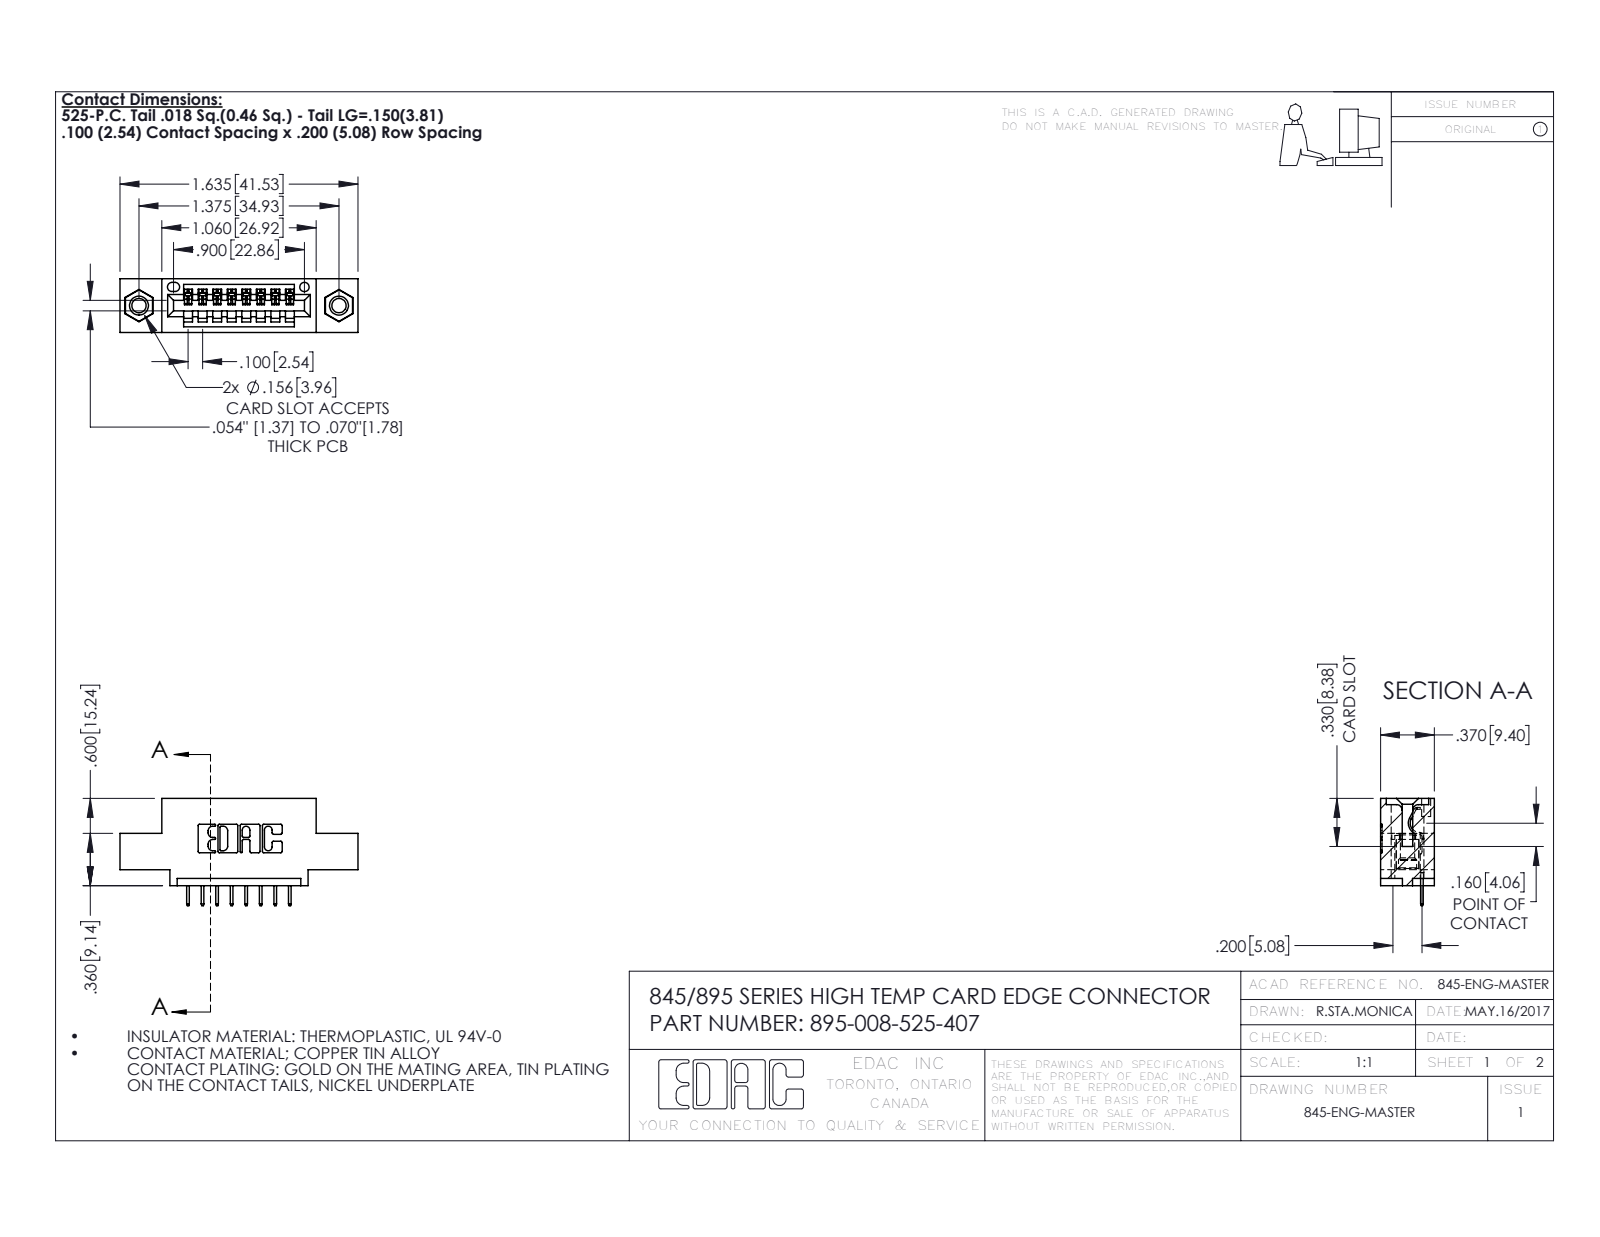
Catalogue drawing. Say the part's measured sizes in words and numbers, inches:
The part is named "895-008-525-407; 345-292-001_345-293-125; 845 Part_0.110 Offset - 0.156 Dia-TI; 345-250-001_345-250-005-103". Its 3-D file was written by "SolidWorks 2020 (CONFIG_CONTROL_DESIGN)". It is 11 solids with 686 faces: 484 planar, 186 cylindrical and 16 other. Overall it measures 1.635 by 0.737 by 0.37 inches. Its volume is 0.216 cubic inches and its surface area 6.597 square inches. Round holes: 2 of diameter 0.098, 2 of diameter 0.125, 2 of diameter 0.156, 1 of diameter 0.064. Round bosses or shafts: 2 of diameter 0.155. Partial cylindrical surfaces (rounded edges, fillets, slot ends): 22 of radius 0.01, 16 of radius 0.006, 6 of radius 0.007, 6 of radius 0.031, 3 of radius 0.026, 2 of radius 0.031, 2 of radius 0.04, 1 of radius 0.014. The main face-to-face distances are 0.2, 0.37, 0.1, 0.072, 0.298, 0.3, 0.16, 0.06, 0.4, 0.04. The hole center spacings are 0.27, 1.144, 1.375.
